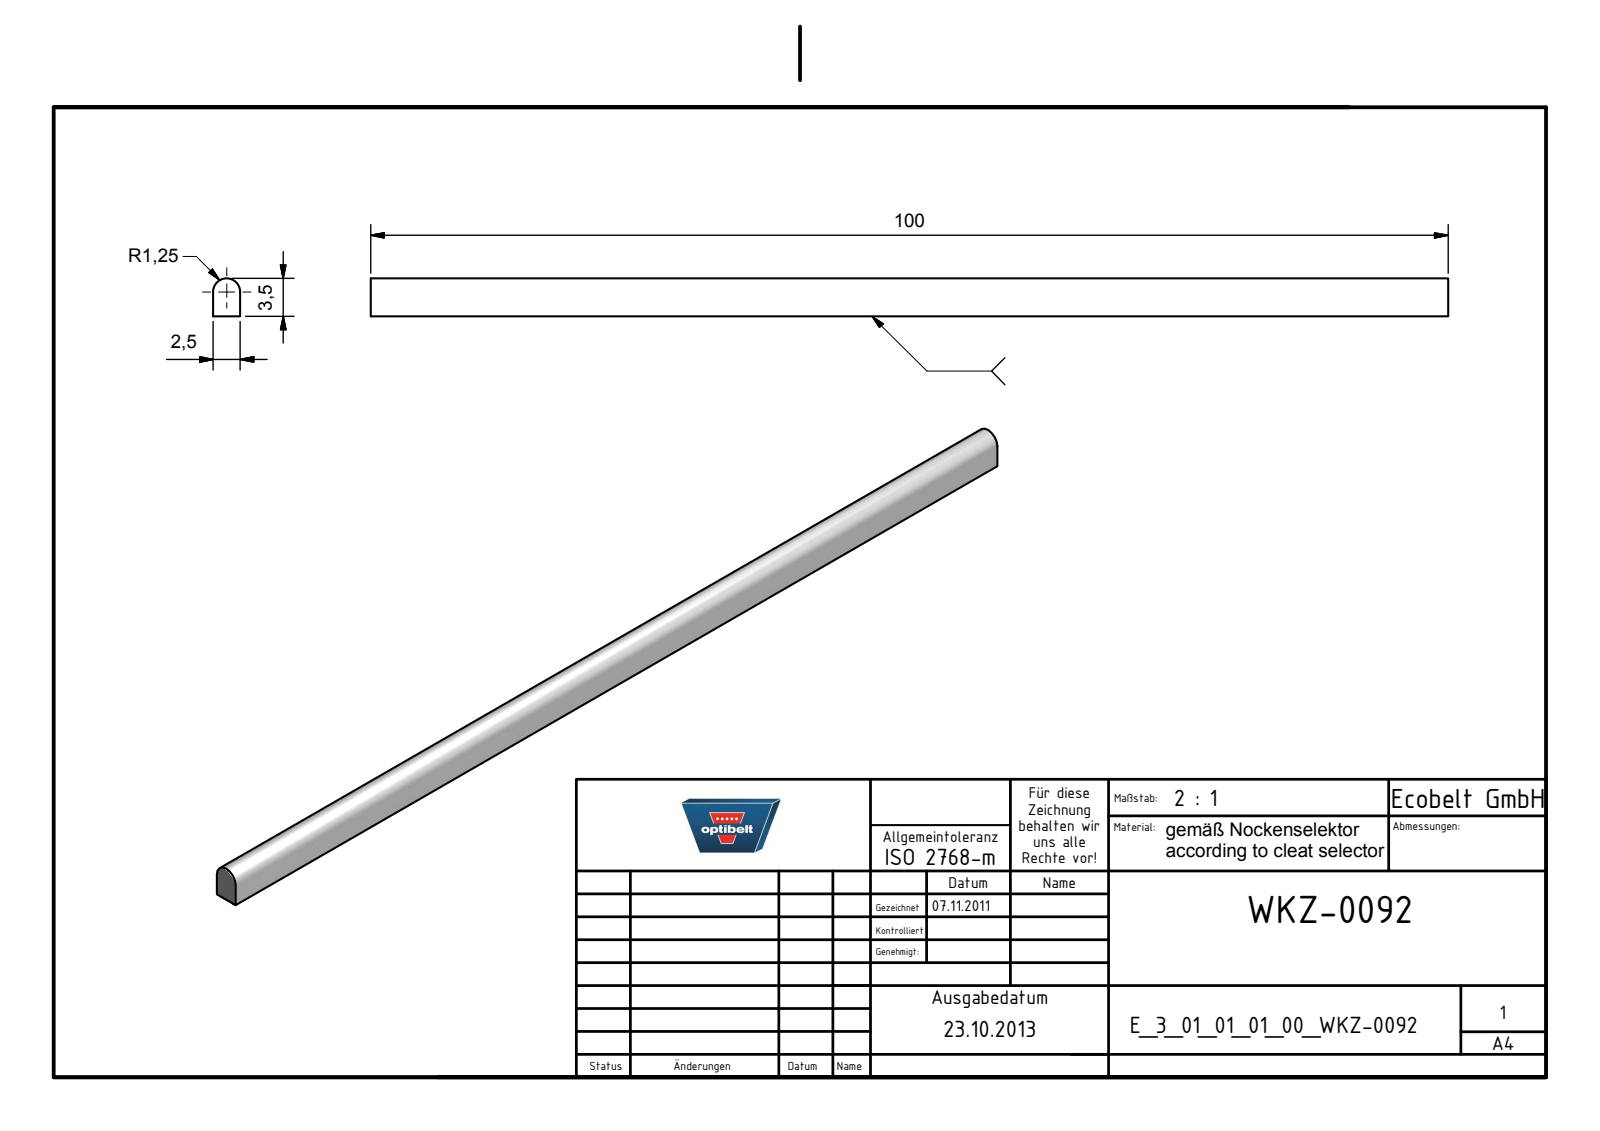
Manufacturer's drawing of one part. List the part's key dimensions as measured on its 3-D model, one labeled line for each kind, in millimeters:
Part name (STEP PRODUCT): E_3_01_01_01_00_WKZ-0092
STEP written by: Autodesk Inventor 2021 (AUTOMOTIVE_DESIGN)
Units: millimetres
Bodies: 1 solid, 6 faces (5 planar, 1 cylindrical, 0 other)
Overall size (bounding box): 100 × 3.5 × 2.5
Volume: 808 mm³ · Surface area: 1 109 mm²
Partial cylindrical surfaces — rounded edges, fillets, slot ends (radius × count): R1.25 ×1
Main face-to-face distances: 2.5, 100
